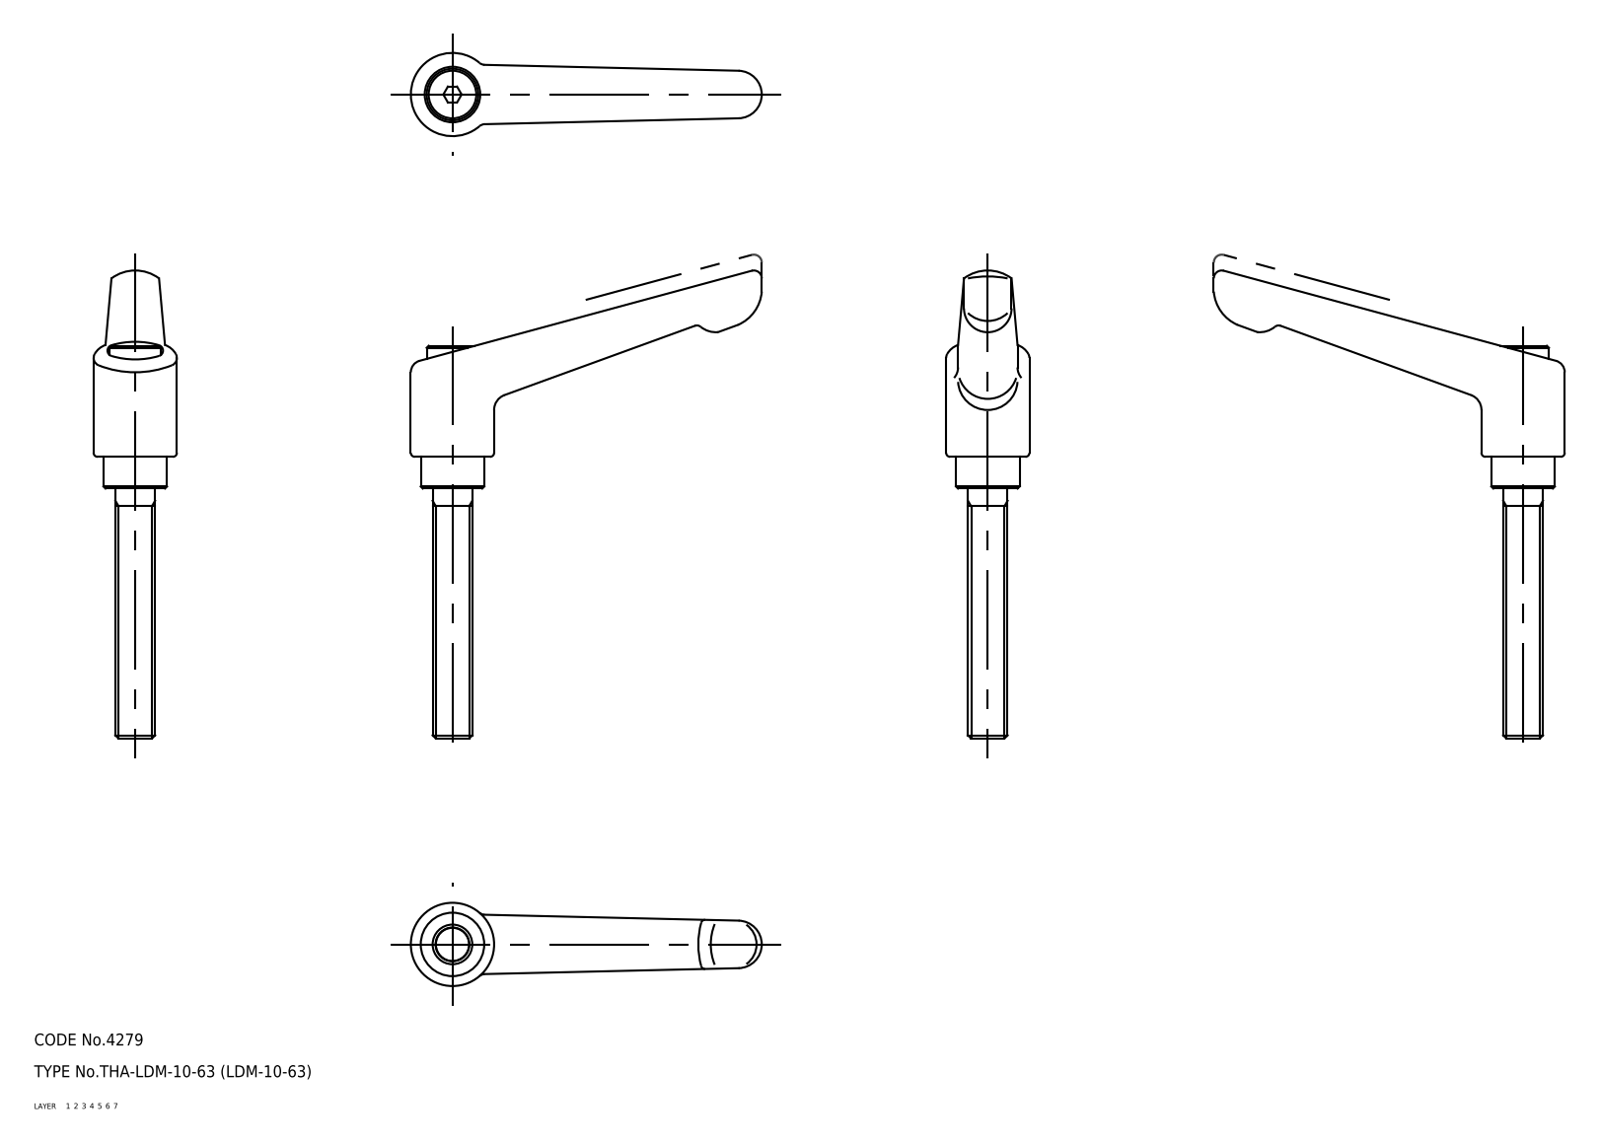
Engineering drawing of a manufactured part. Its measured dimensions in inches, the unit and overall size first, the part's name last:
Units: inches
Overall size (bounding box): 4.646 × 3.484 × 0.827
Volume: 1.483 in³ · Surface area: 15.98 in²
Bodies: 3 solids, 75 faces (0 planar, 0 cylindrical, 75 other)
Part name (STEP PRODUCT): sleeve; screw; handle; LDM_10_63_26176_36
STEP written by: CADfix (AUTOMOTIVE_DESIGN)
